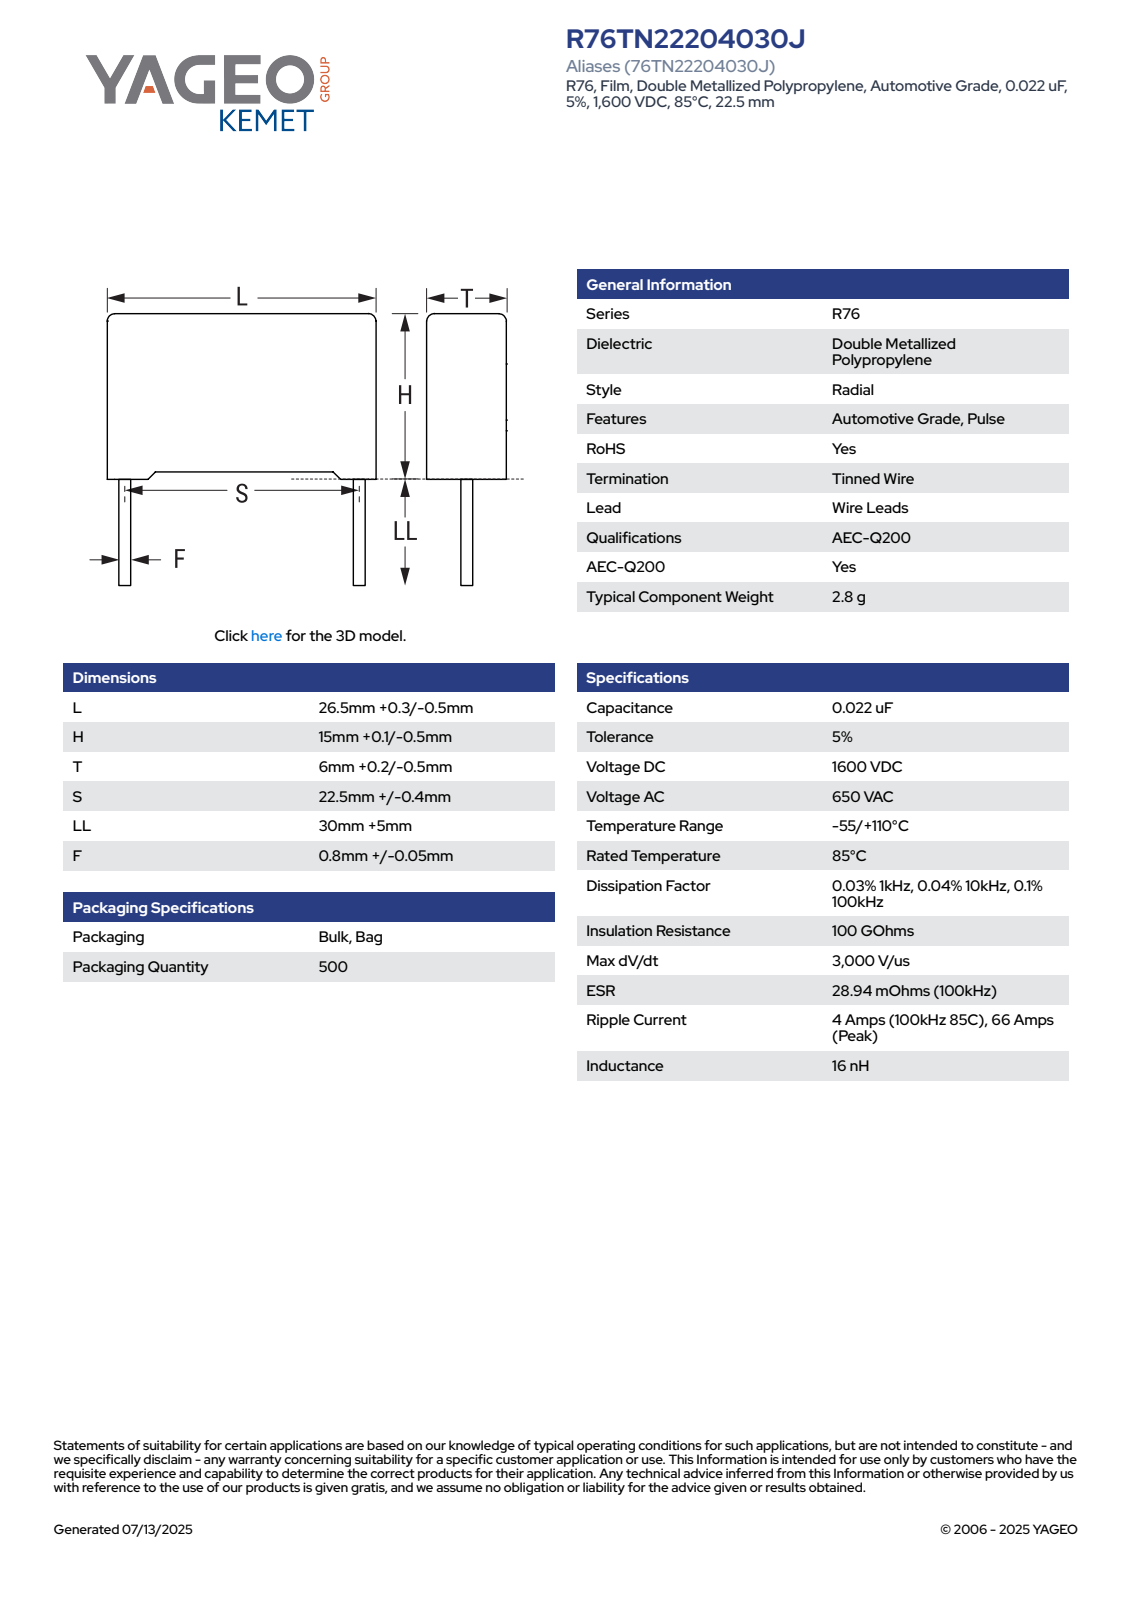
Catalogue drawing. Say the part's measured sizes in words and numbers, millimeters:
The part is named "CFR_RB2_26.5X15X6_L26.8H15.1T6.2S22.5LL35F0.85". Its 3-D file was written by "SolidWorks 2021 (AUTOMOTIVE_DESIGN)". It is 4 solids with 85 faces: 77 planar, 8 cylindrical and 0 other. Overall it measures 50.1 by 26.8 by 6.21 millimeters. Its volume is 2 446 cubic millimeters and its surface area 1 565 square millimeters. Round bosses or shafts: 2 of diameter 0.85. Partial cylindrical surfaces (rounded edges, fillets, slot ends): 4 of radius 0.5. The main face-to-face distances are 6.2, 14.35, 26.8, 14.58, 0.89, 0.52, 0.75, 15.1, 5.31, 4.42.
